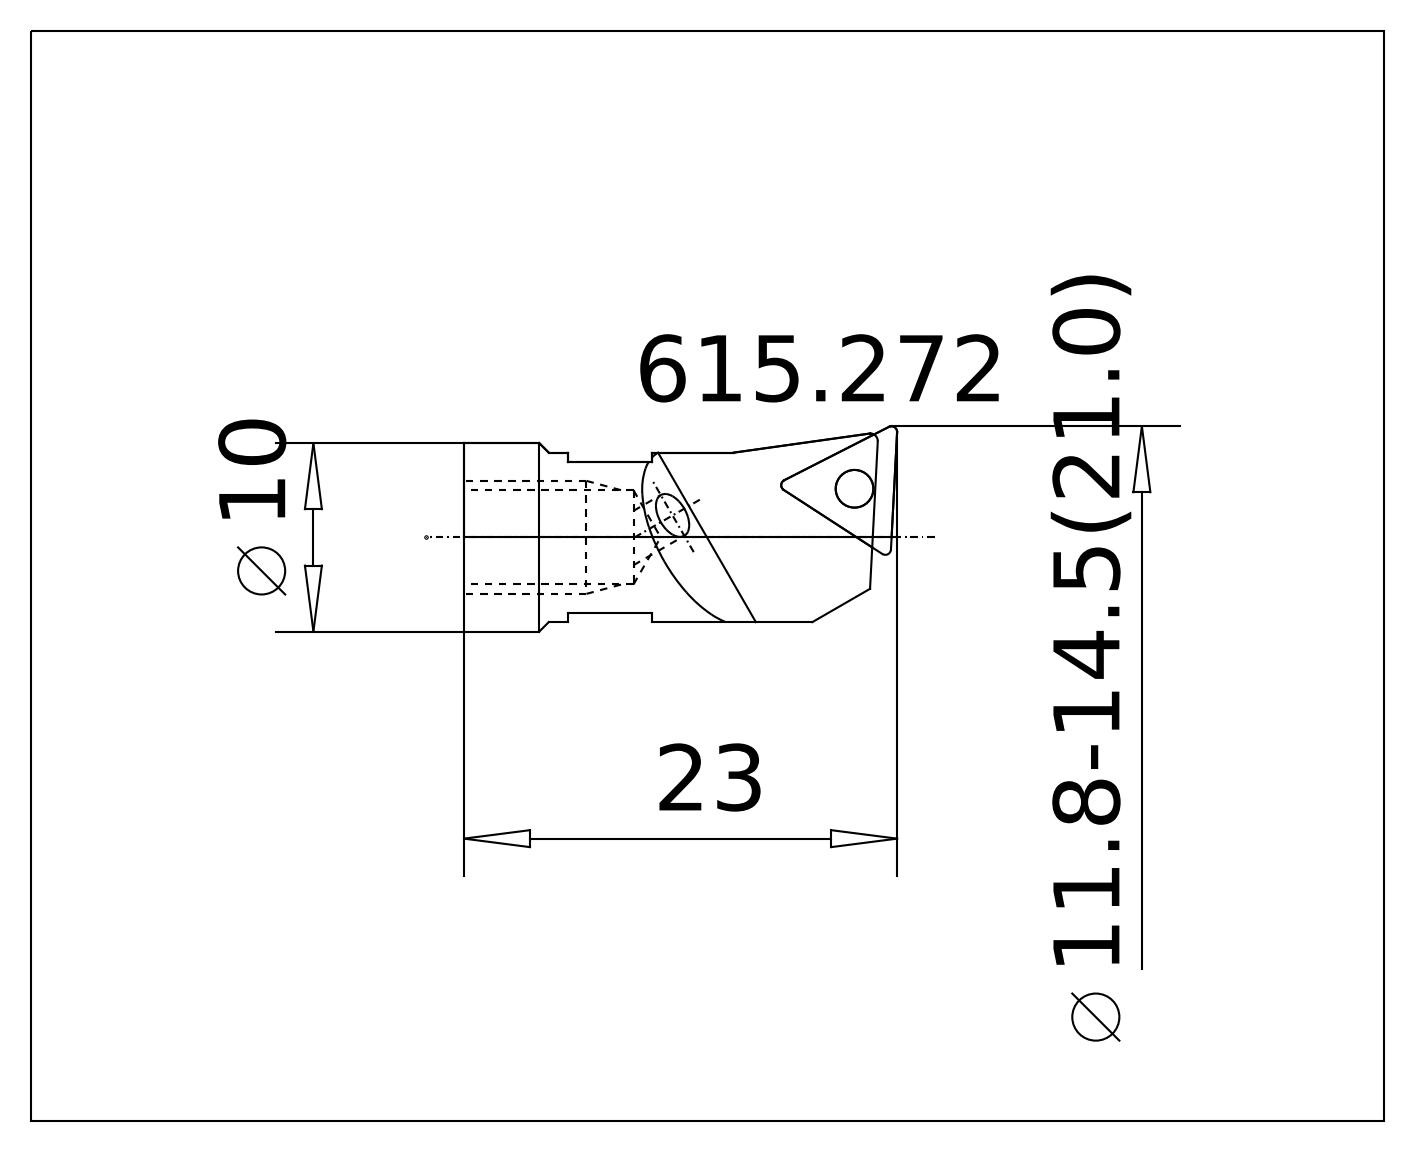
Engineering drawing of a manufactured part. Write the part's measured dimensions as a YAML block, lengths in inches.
part_name: "615.272 Kaiser E12 TP07|651.735 Kaiser TPGT 070203 K10C;Kombinieren1; 615.272 Kaiser E12 TP07|694.103 Kaiser ETL M2x4.8 T6 IP 10S;Kreismuster1; 615.272 Kaiser E12 TP07|615.272 Kaiser E12 TP07;Verrundung5"
step_written_by: "ACIS (automotive_design)"
units: inches
bodies: {solids: 3, faces: 124, planar: 29, cylindrical: 52, other: 43}
overall_size: [0.906, 0.427, 0.394]
volume: 0.056
surface_area: 1.64
round_holes:
  - {diameter: 0.061, count: 1}
  - {diameter: 0.091, count: 1}
  - {diameter: 0.098, count: 1}
  - {diameter: 0.197, count: 1}
  - {diameter: 0.236, count: 1}
round_bosses_or_shafts:
  - {diameter: 0.394, count: 1}
  - {diameter: 0.354, count: 1}
  - {diameter: 0.106, count: 1}
  - {diameter: 0.079, count: 1}
partial_cylinders:
  - {radius: 0.006, count: 6}
  - {radius: 0.012, count: 6}
  - {radius: 0.008, count: 4}
  - {radius: 0.043, count: 1}
  - {radius: 0.059, count: 1}
  - {radius: 0.079, count: 1}
  - {radius: 0.118, count: 1}
  - {radius: 0.173, count: 1}
face_to_face_distances: [0.098, 0.315, 0.177, 0.276, 0.276, 0.087, 0.068, 0.03, 0.091, 0.159]
